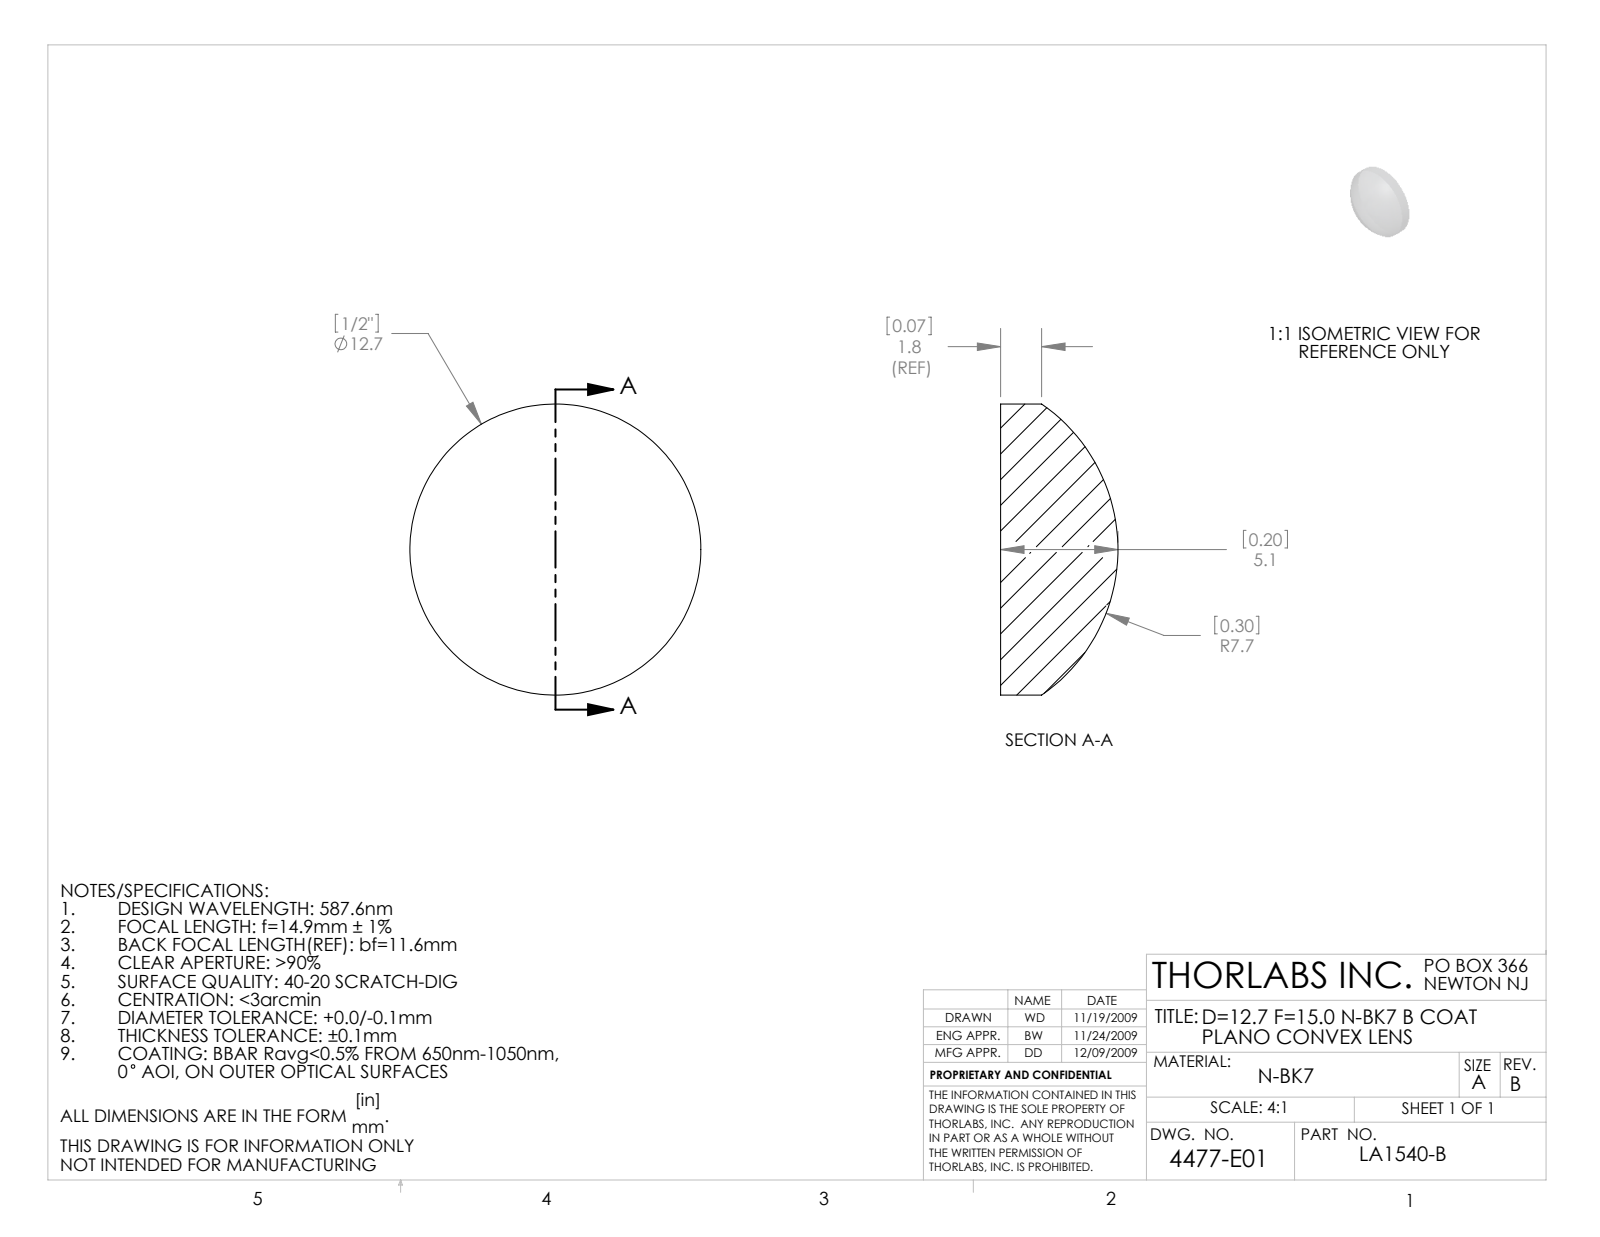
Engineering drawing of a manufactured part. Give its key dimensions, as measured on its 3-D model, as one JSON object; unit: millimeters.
{"part_name": "4477-E0W", "step_written_by": "SolidWorks 2009 (AUTOMOTIVE_DESIGN)", "units": "millimeters", "bodies": {"solids": 1, "faces": 5, "planar": 1, "cylindrical": 2, "other": 2}, "overall_size": [12.7, 12.7, 5.12], "volume_mm3": 457, "surface_area_mm2": 360, "round_bosses_or_shafts": [[12.7, 1]]}
